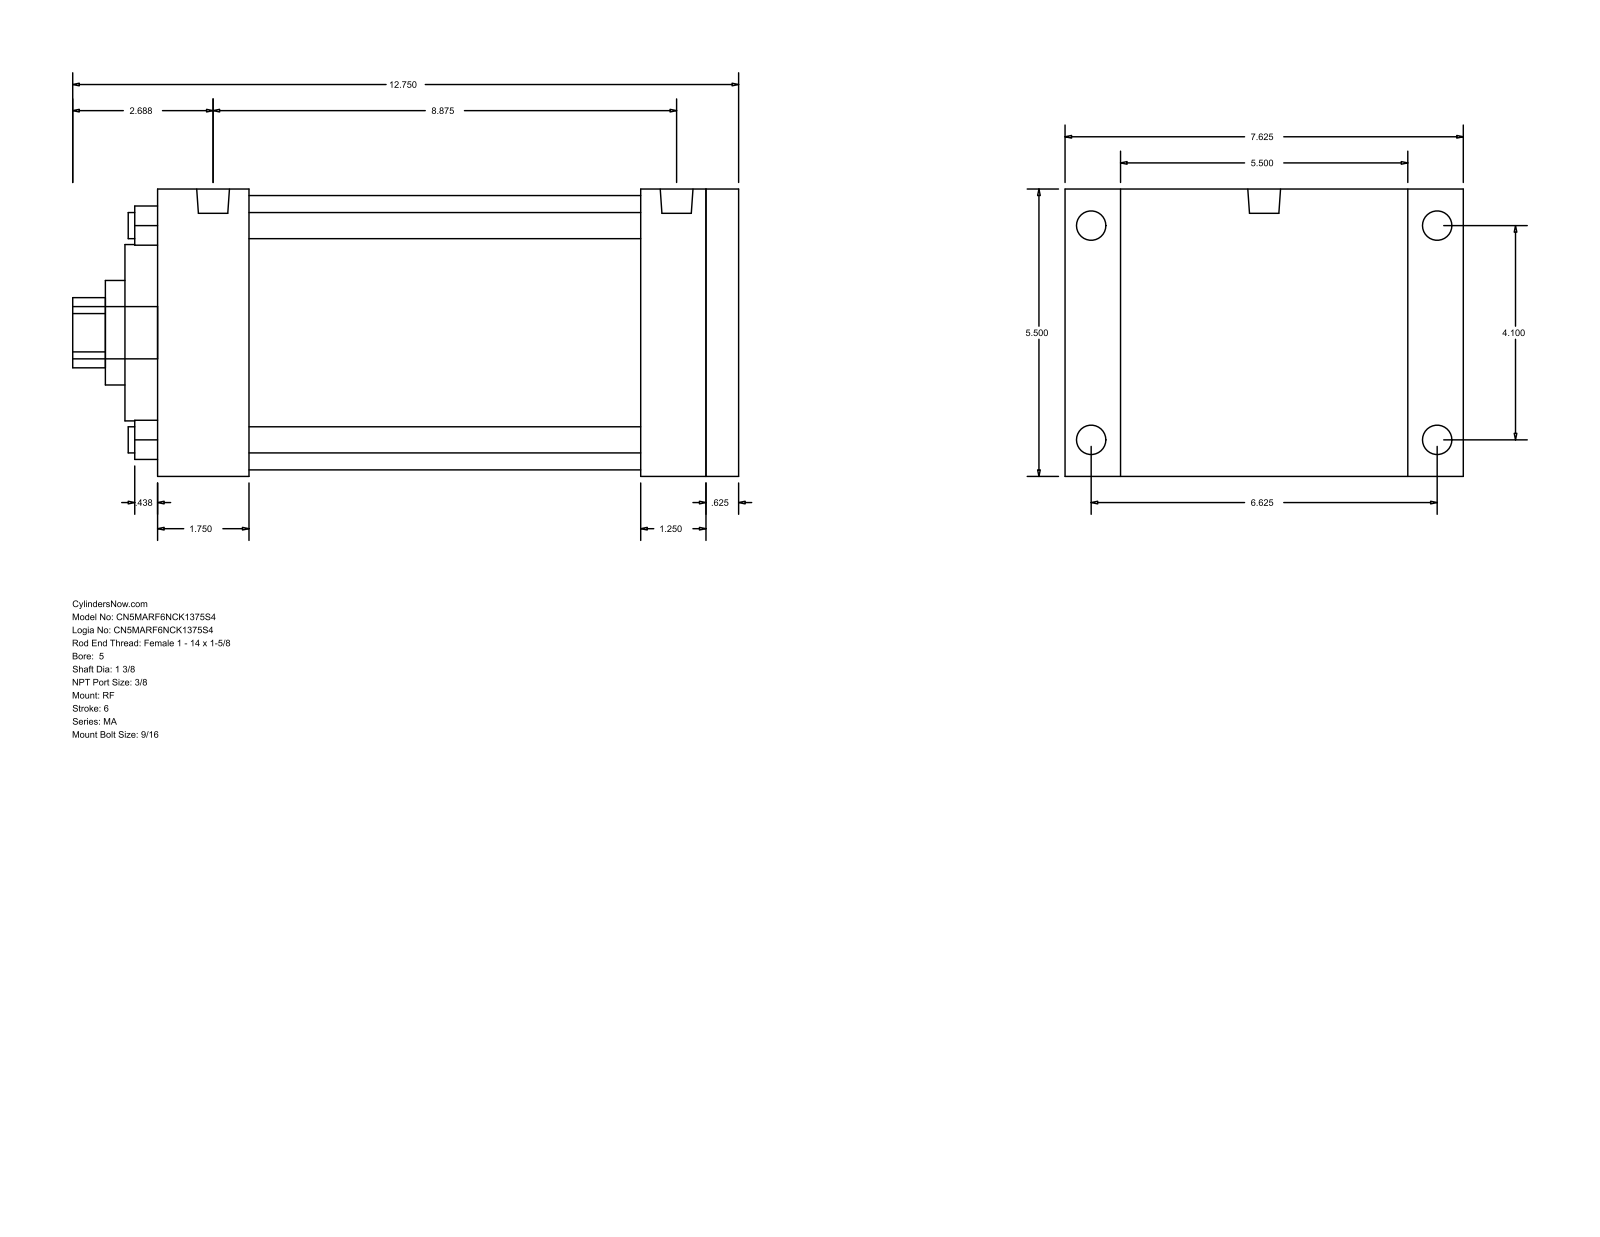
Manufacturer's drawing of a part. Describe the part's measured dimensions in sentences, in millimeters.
The part is named "MA_RF__0500_1.375". Its 3-D file was written by "GSSL Pune (CONFIG_CONTROL_DESIGN)". It is 0 solids with 94 faces: 65 planar, 29 cylindrical and 0 other. Overall it measures 323.85 by 193.68 by 139.7 millimeters. Round holes: 4 of diameter 12.7, 1 of diameter 34.92, 1 of diameter 50.8, 1 of diameter 85.72, 1 of diameter 133.35. Round bosses or shafts: 4 of diameter 14.29, 4 of diameter 11.11, 2 of diameter 15.93, 1 of diameter 25.4. Partial cylindrical surfaces (rounded edges, fillets, slot ends): 1 of radius 17.06. The main face-to-face distances are 139.7, 282.58, 15.87, 266.71, 44.45, 222.26, 238.13, 234.96, 190.51, 31.75. The hole center spacings are 73.64, 104.14, 147.28.
